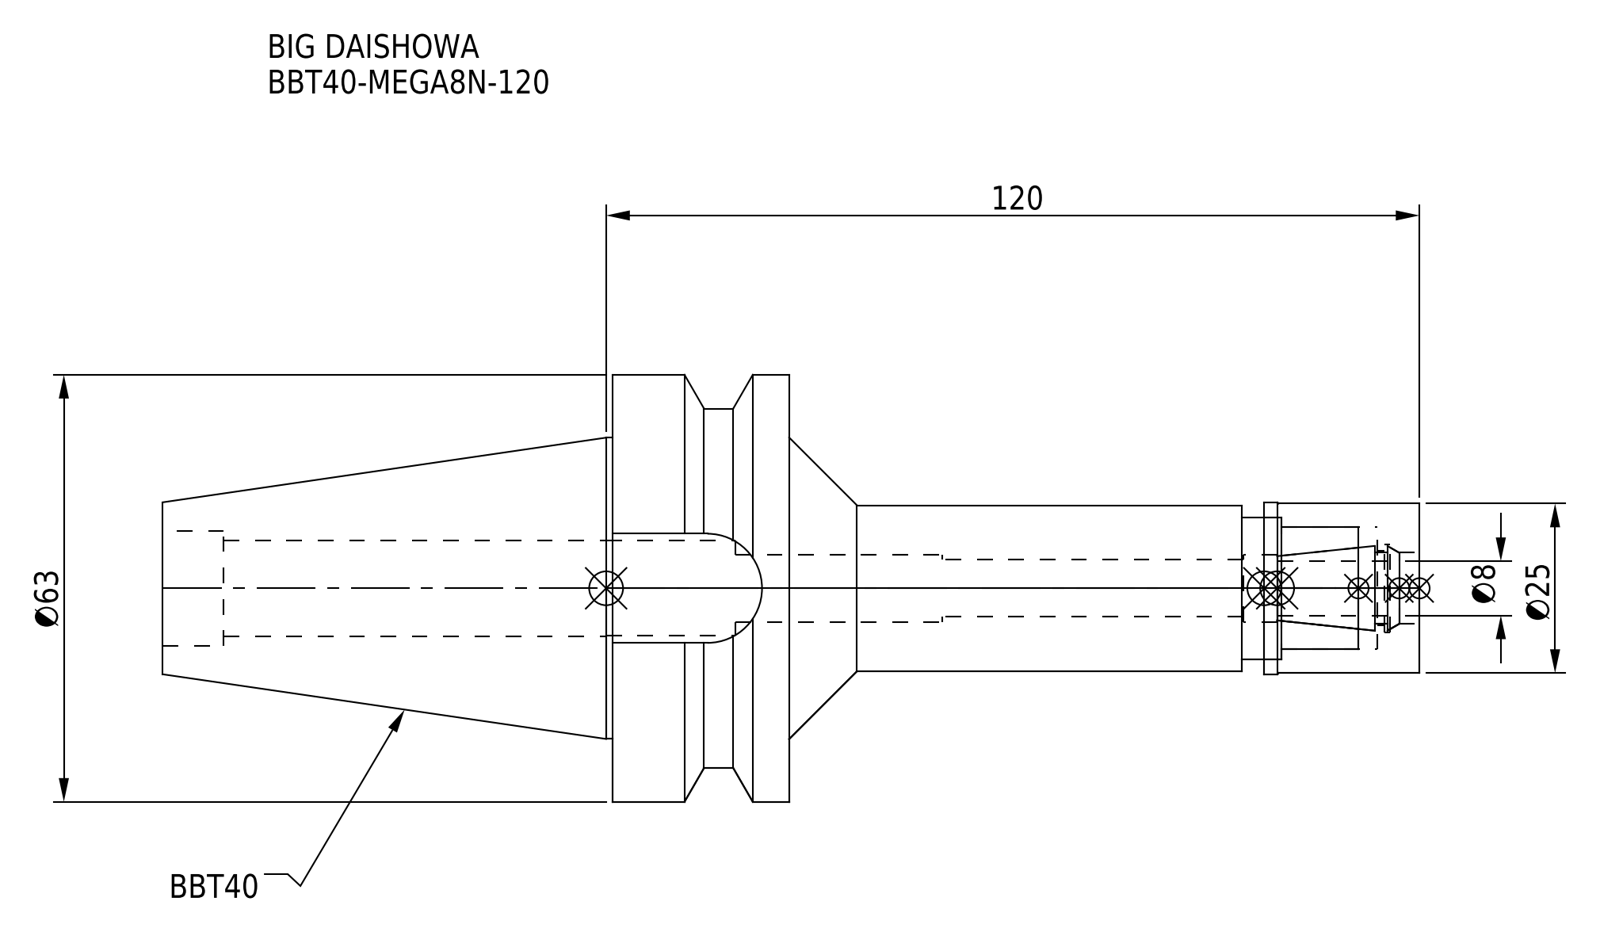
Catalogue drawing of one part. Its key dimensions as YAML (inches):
part_name: "BBT40MN08120-080_ASM.stp; BBT40-MEGA8N-120_1.stp; BBT40-MEGA8N-120-080-FreeParts; DXF_TEMP_ASSY_ASM_4_ASM.stp (+3 more)"
step_written_by: "SolidWorks 2019 (CONFIG_CONTROL_DESIGN)"
units: inches
bodies: {solids: 2, faces: 80, planar: 24, cylindrical: 42, other: 14}
overall_size: [7.299, 2.48, 2.48]
volume: 9.935
surface_area: 54.12
round_holes:
  - {diameter: 0.331, count: 1}
  - {diameter: 0.394, count: 1}
  - {diameter: 0.413, count: 1}
  - {diameter: 0.433, count: 1}
  - {diameter: 0.512, count: 1}
  - {diameter: 0.551, count: 1}
  - {diameter: 0.559, count: 1}
  - {diameter: 0.669, count: 1}
  - {diameter: 0.709, count: 1}
  - {diameter: 0.827, count: 1}
round_bosses_or_shafts:
  - {diameter: 2.48, count: 1}
  - {diameter: 2.087, count: 1}
  - {diameter: 1.75, count: 1}
  - {diameter: 0.996, count: 1}
  - {diameter: 0.984, count: 1}
  - {diameter: 0.965, count: 1}
partial_cylinders:
  - {radius: 0.317, count: 1}
face_to_face_distances: [1.024, 3.661, 4.685, 1.772, 7.299, 3.638, 2.614, 0.354, 6.945, 0.634]
